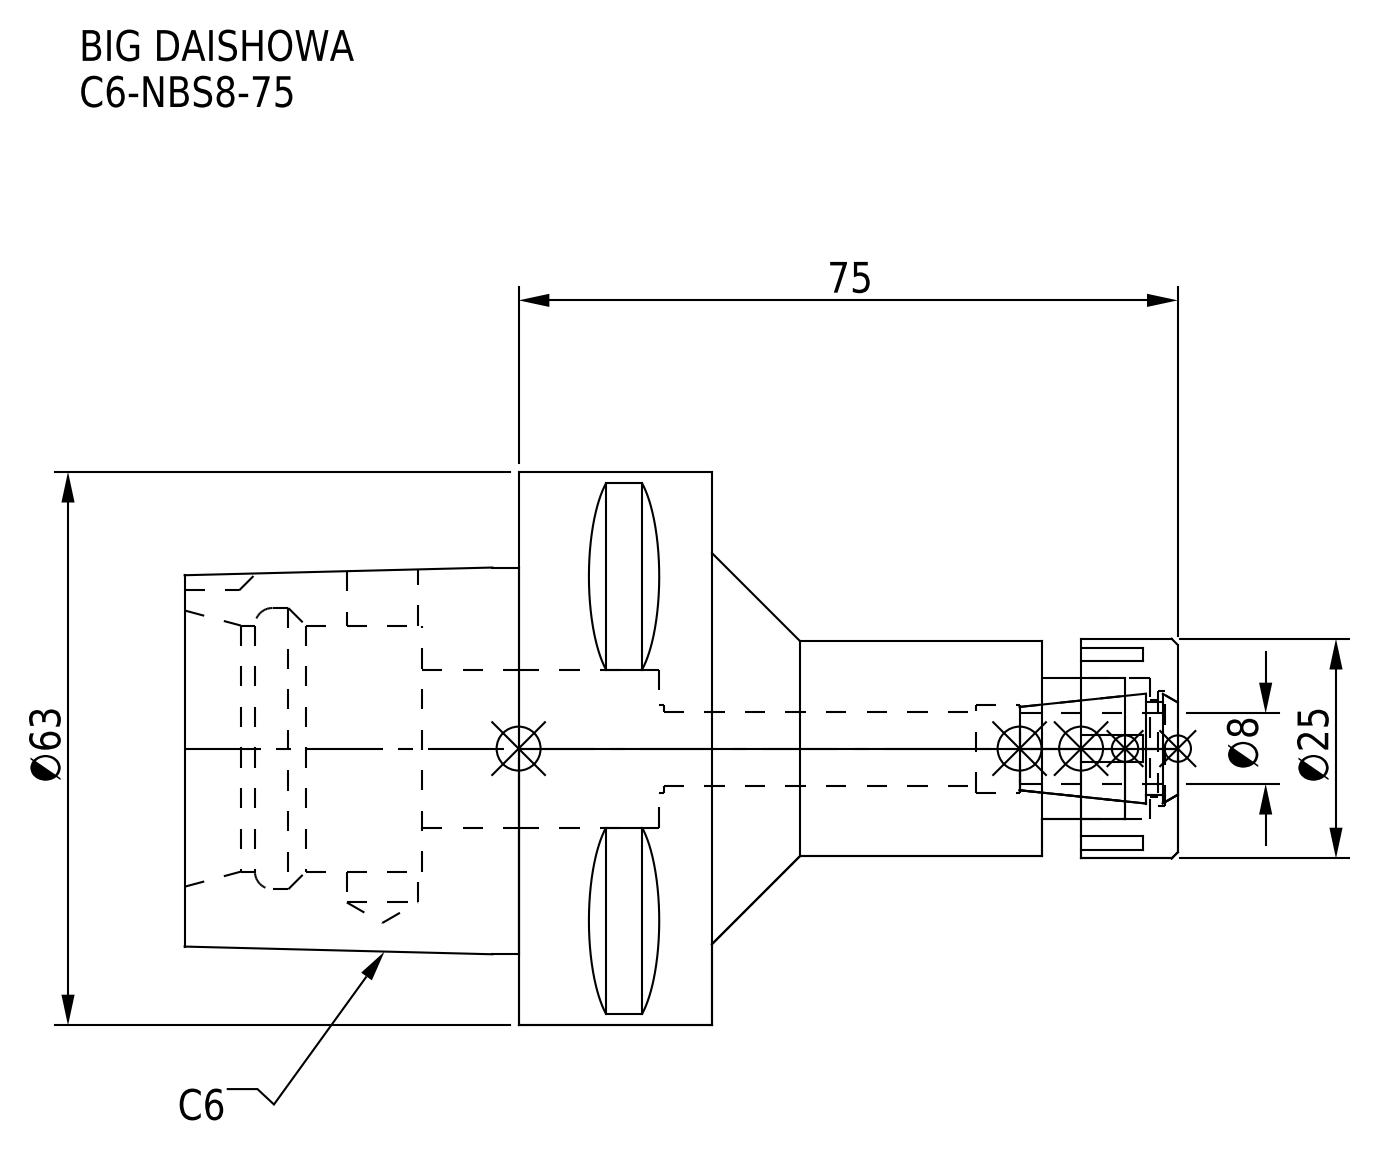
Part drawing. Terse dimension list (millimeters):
name: DXF_TEMP_ASSY_ASM_4_ASM.stp; C6-NBS8-75-FreeParts; C6-NBS8-75; C6-NBS8-75-080_ASM.stp (+3 more)
written by: SolidWorks 2019 (CONFIG_CONTROL_DESIGN)
unit: mm
bodies: 2 solids, 112 faces (61 planar, 33 cylindrical, 18 other)
size: 113 × 63 × 63
volume: 120 846 mm³; area: 26 888 mm²
holes: 1× ⌀8.1, 1× ⌀8.4, 1× ⌀10, 1× ⌀11, 1× ⌀13, 1× ⌀16, 1× ⌀18, 1× ⌀28, 1× ⌀32
bosses: 1× ⌀63, 1× ⌀25, 1× ⌀24.5
rounds: 1× R5
face distances: 22, 11, 75, 27, 60, 38, 53, 33, 86, 113
